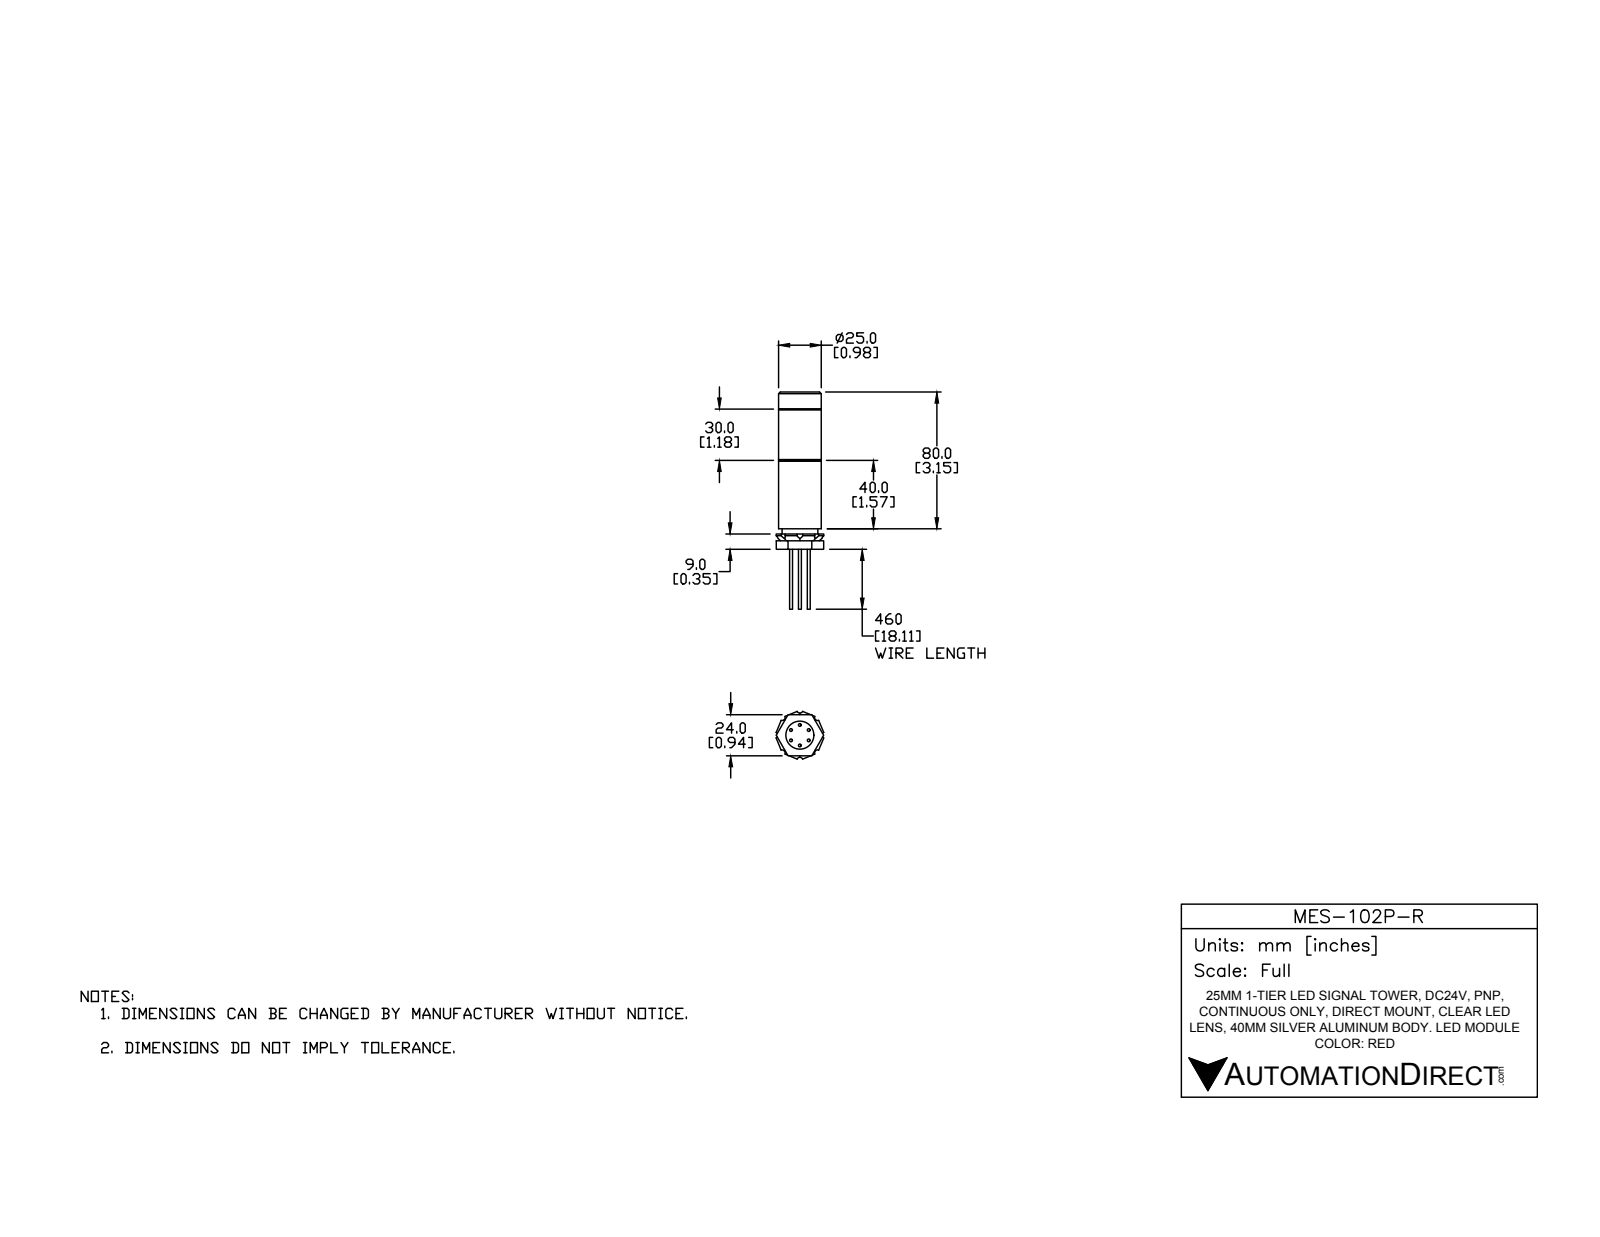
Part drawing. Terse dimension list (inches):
name: MES-102P-R
written by: SolidWorks 2016 (AUTOMOTIVE_DESIGN)
unit: in
bodies: 12 solids, 132 faces (71 planar, 47 cylindrical, 14 other)
size: 5 × 1.098 × 1.098
volume: 2.053 in³; area: 28.93 in²
holes: 1× ⌀0.126, 1× ⌀0.303, 1× ⌀0.646, 1× ⌀0.709, 1× ⌀0.815, 1× ⌀0.827
bosses: 6× ⌀0.067, 1× ⌀0.984, 1× ⌀0.823, 1× ⌀0.63, 1× ⌀0.197
rounds: 8× R0.069
face distances: 1.181, 1.575, 0.276, 1.85, 1.457, 0.394, 1.772, 2.047, 3.228, 3.622
